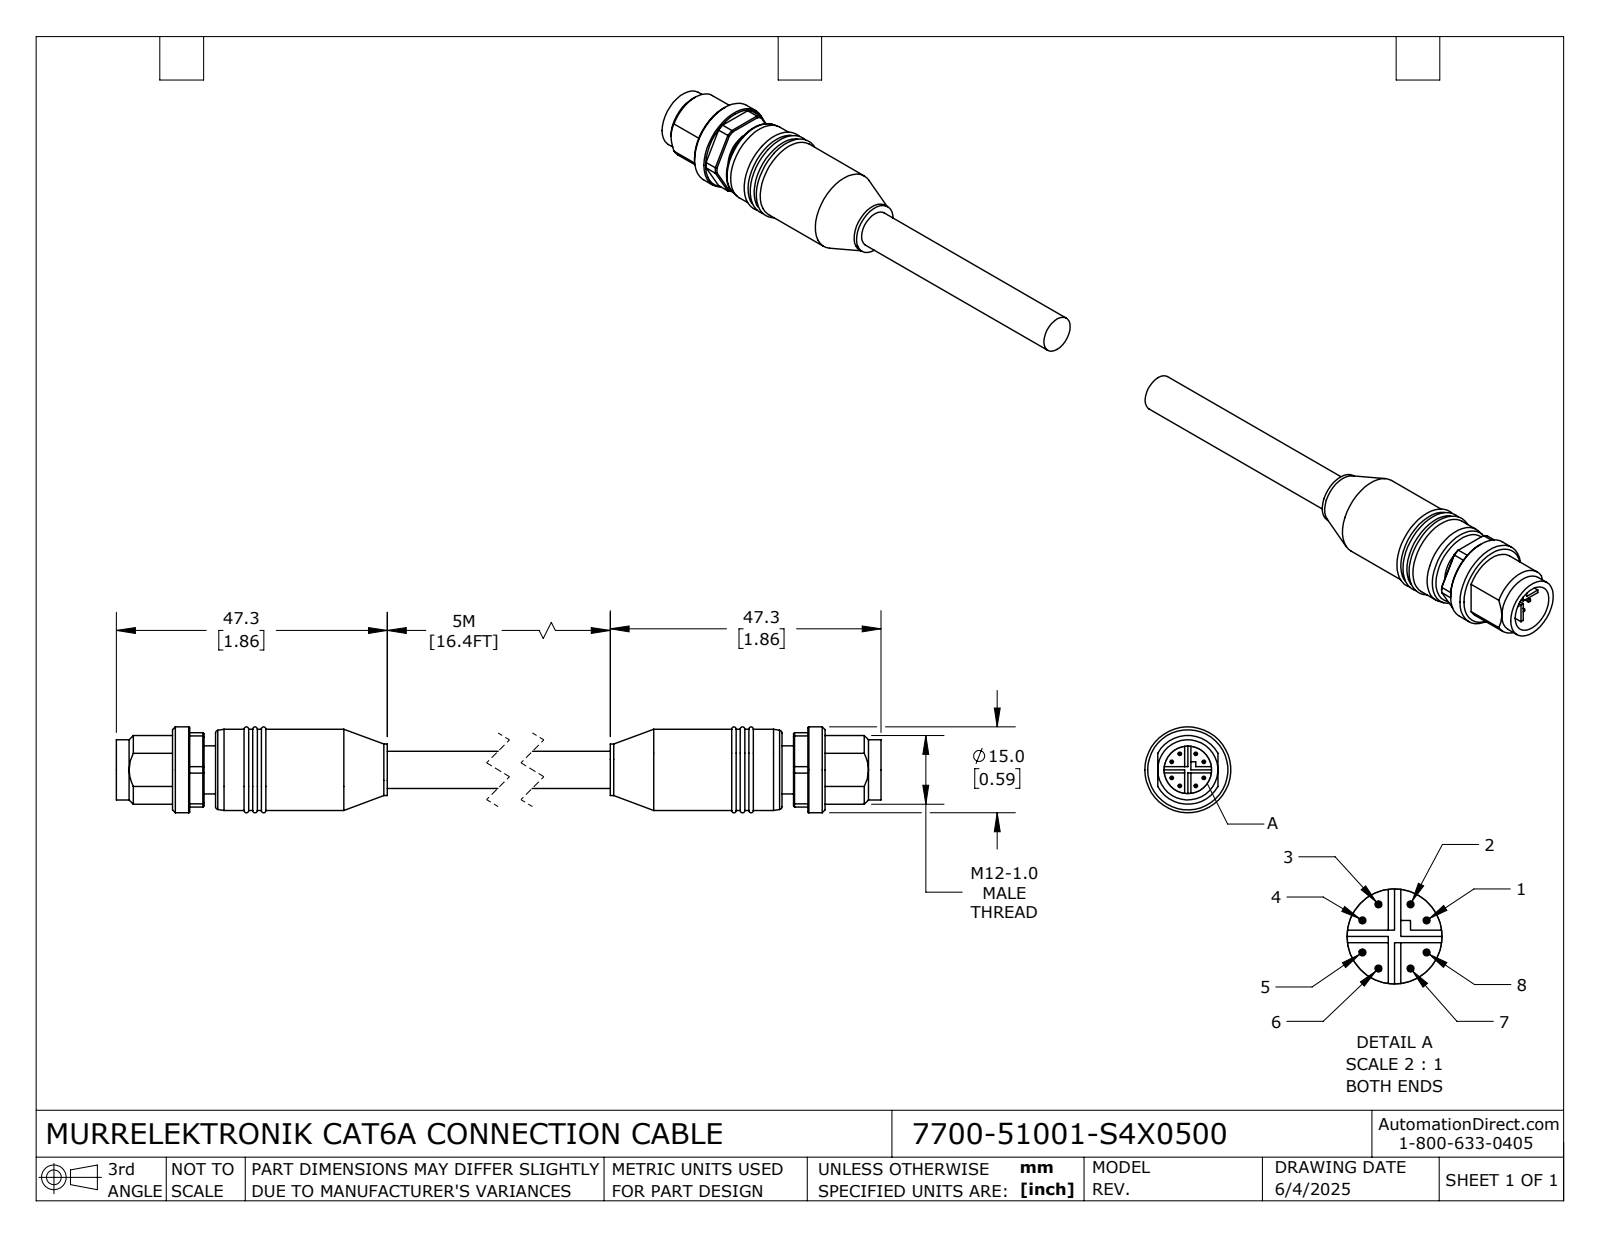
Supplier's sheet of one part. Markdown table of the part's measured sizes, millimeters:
| quantity | value |
| --- | --- |
| part name | 7700-51001-S4X0500_MALE; 7700-51001-S4X0500 |
| STEP written by | SolidWorks 2024 (CONFIG_CONTROL_DESIGN) |
| units | millimeters |
| bodies | 2 solids, 282 faces (112 planar, 88 cylindrical, 82 other) |
| overall size | 209.6 × 15 × 15 |
| volume | 14 953 mm³ |
| surface area | 7 635 mm² |
| round holes (diameter × count) | 8.3 × 1 |
| round bosses / shafts (diameter × count) | 0.6 × 8, 15 × 1, 14.2 × 1, 10.5 × 1, 9 × 1, 8.4 × 1, 6.5 × 1 |
| partial cylindrical surfaces (radius × count) | 6 × 1, 7.2 × 1 |
| main face-to-face distances | 4.7, 5.8, 2, 177, 1.1, 5.5, 13, 7.5, 182.5, 184.5 |
